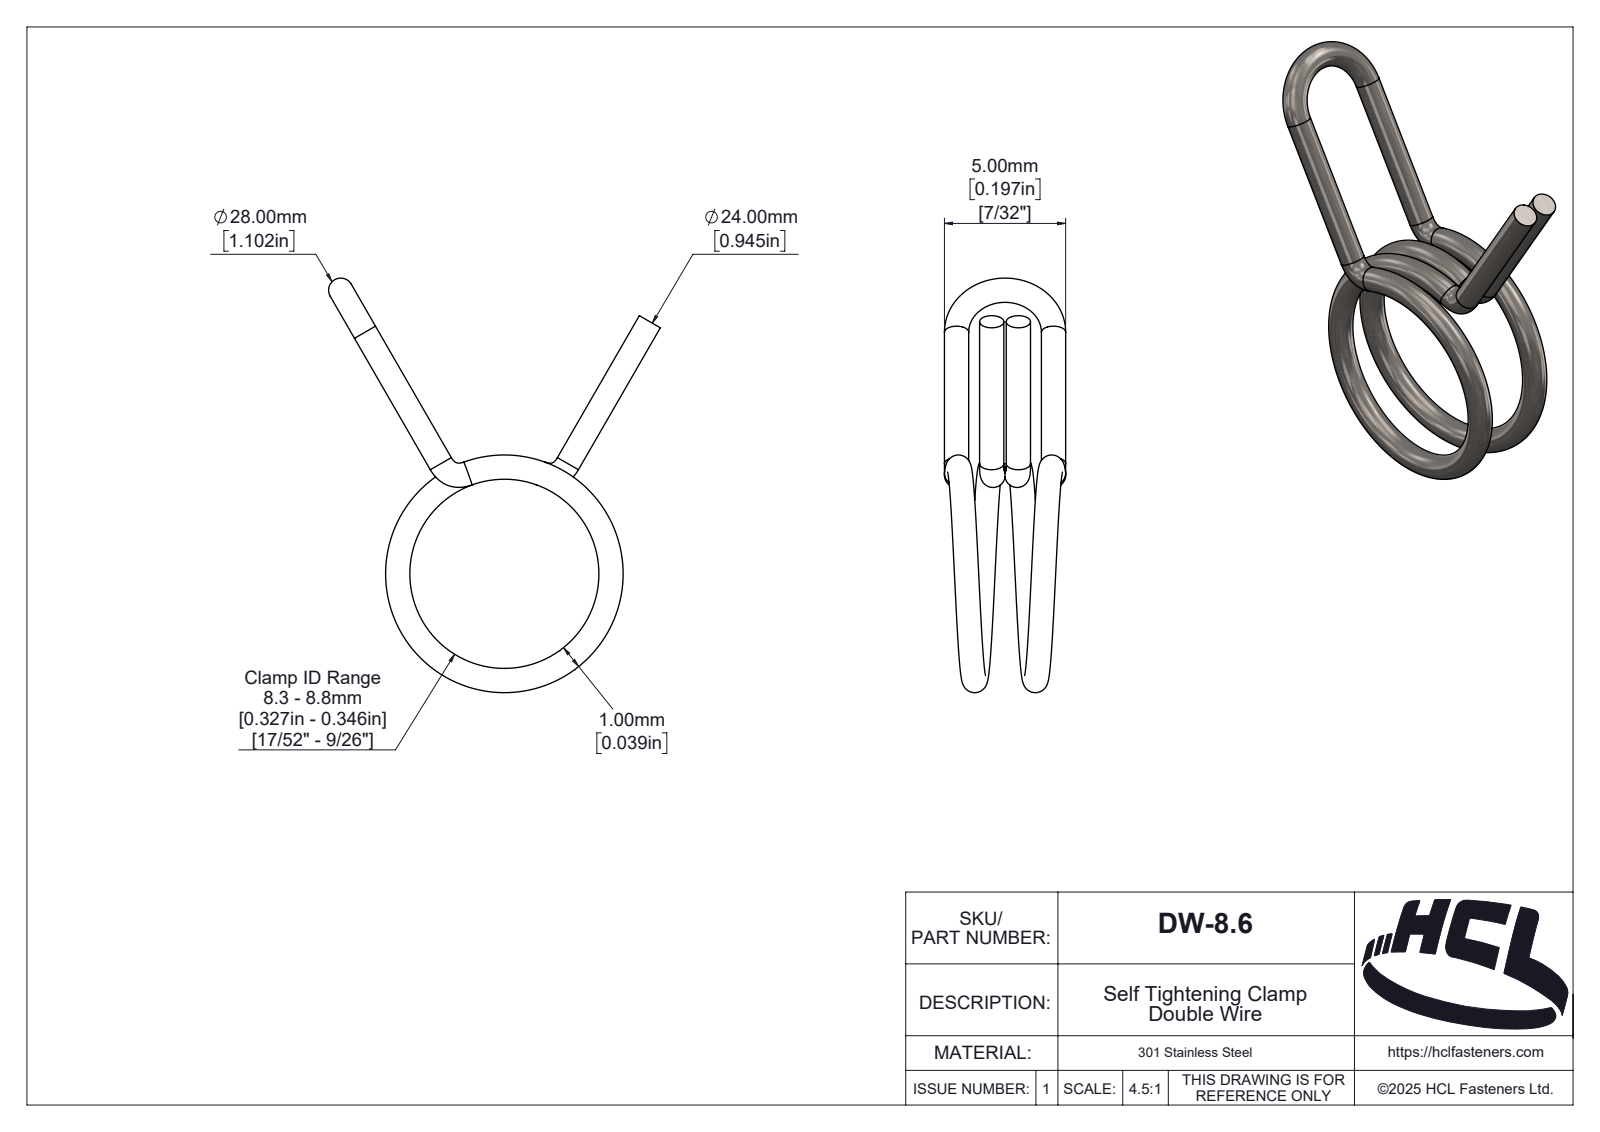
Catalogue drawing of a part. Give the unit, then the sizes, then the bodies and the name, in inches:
Units: inches
Overall size (bounding box): 0.673 × 0.539 × 0.197
Round bosses / shafts (diameter × count): ⌀0.039 ×4
Partial cylindrical surfaces — rounded edges, fillets, slot ends (radius × count): R0.006 ×1, R0.008 ×1, R0.008 ×1, R0.01 ×1, R0.014 ×1, R0.019 ×1, R0.024 ×1, R0.027 ×1
Volume: 0.005 in³ · Surface area: 0.485 in²
Bodies: 1 solid, 125 faces (14 planar, 53 cylindrical, 58 other)
Part name (STEP PRODUCT): DW-8.6
STEP written by: SolidWorks 2025 (AUTOMOTIVE_DESIGN)
